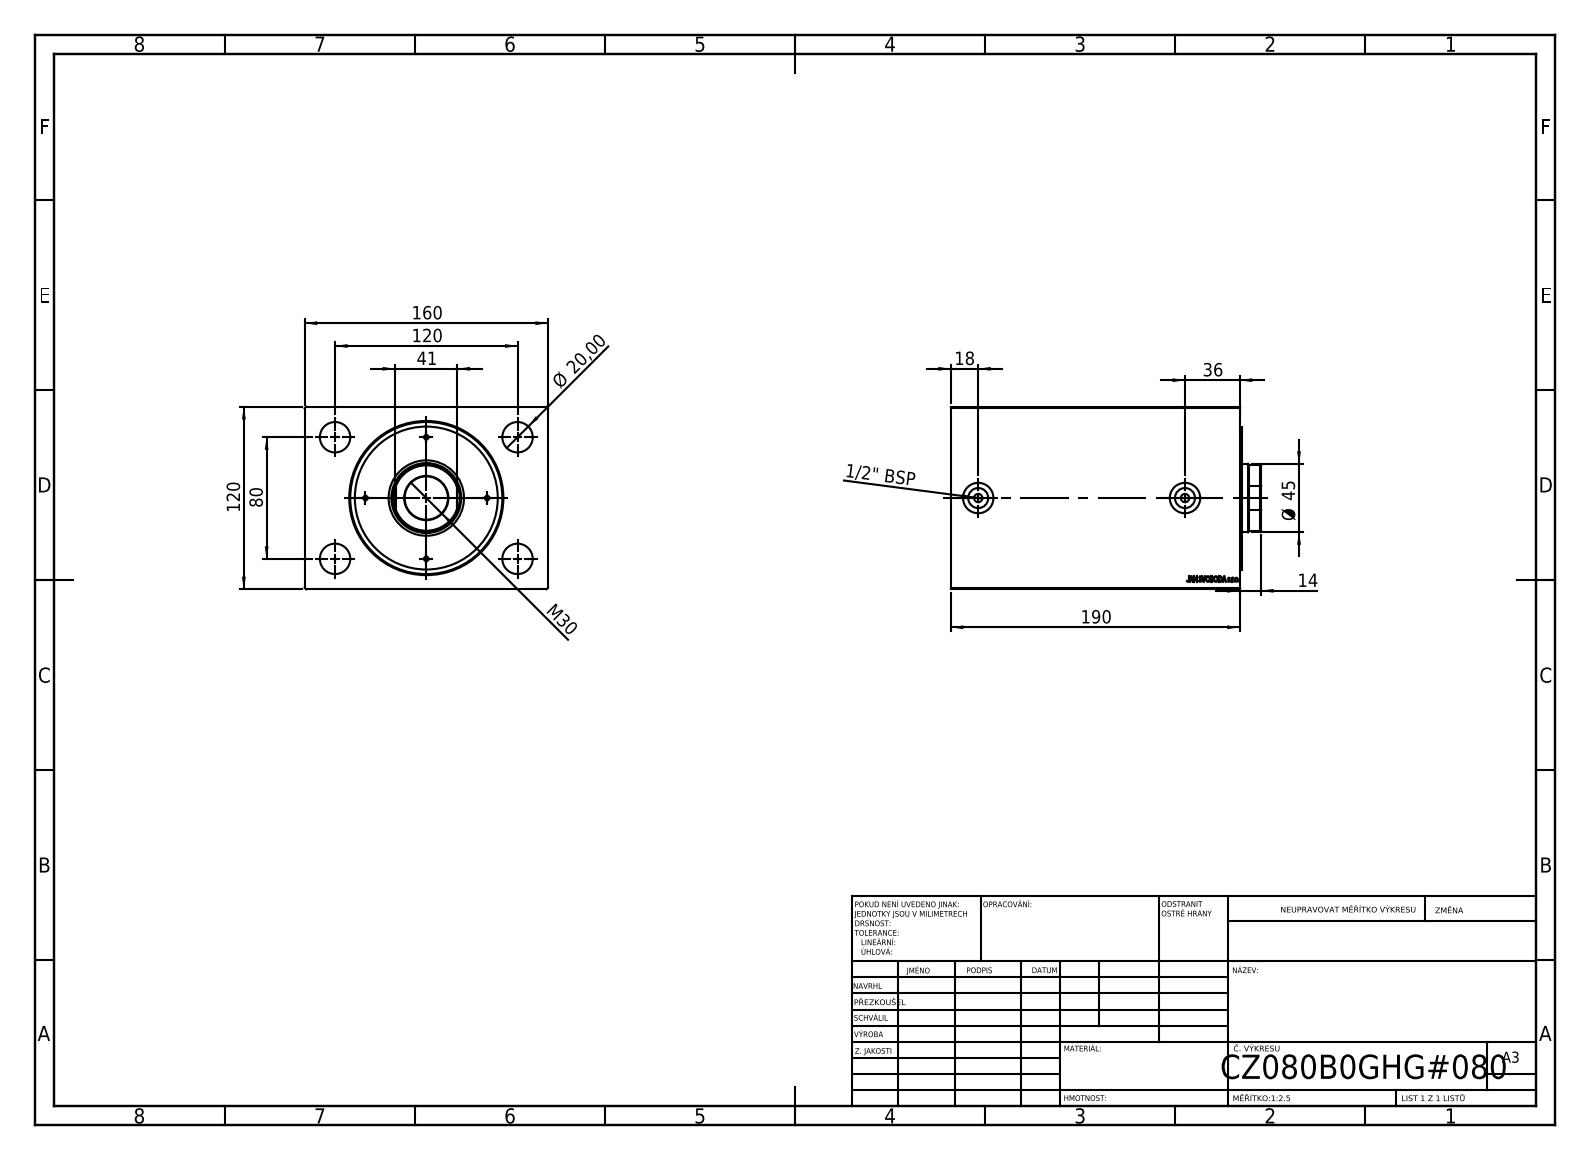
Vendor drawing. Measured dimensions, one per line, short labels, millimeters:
name: V500CZ; V500CZ_B_VC
written by: SolidWorks 2019 (CONFIG_CONTROL_DESIGN)
unit: mm
bodies: 3 solids, 874 faces (400 planar, 58 cylindrical, 416 other)
size: 204 × 160 × 120
volume: 3 287 000 mm³; area: 266 922 mm²
holes: 6× ⌀20, 4× ⌀3, 2× ⌀5.5, 2× ⌀13.16, 1× ⌀28.5, 1× ⌀36, 1× ⌀45, 1× ⌀46, 1× ⌀80, 1× ⌀100
bosses: 1× ⌀94
rounds: 1× R22
face distances: 120, 160, 190, 164.7, 25.3, 14, 1.8, 12.2, 152.5, 177.8
hole spacings: 40, 44.72, 56.57, 60, 72.11, 80, 100, 107.7
